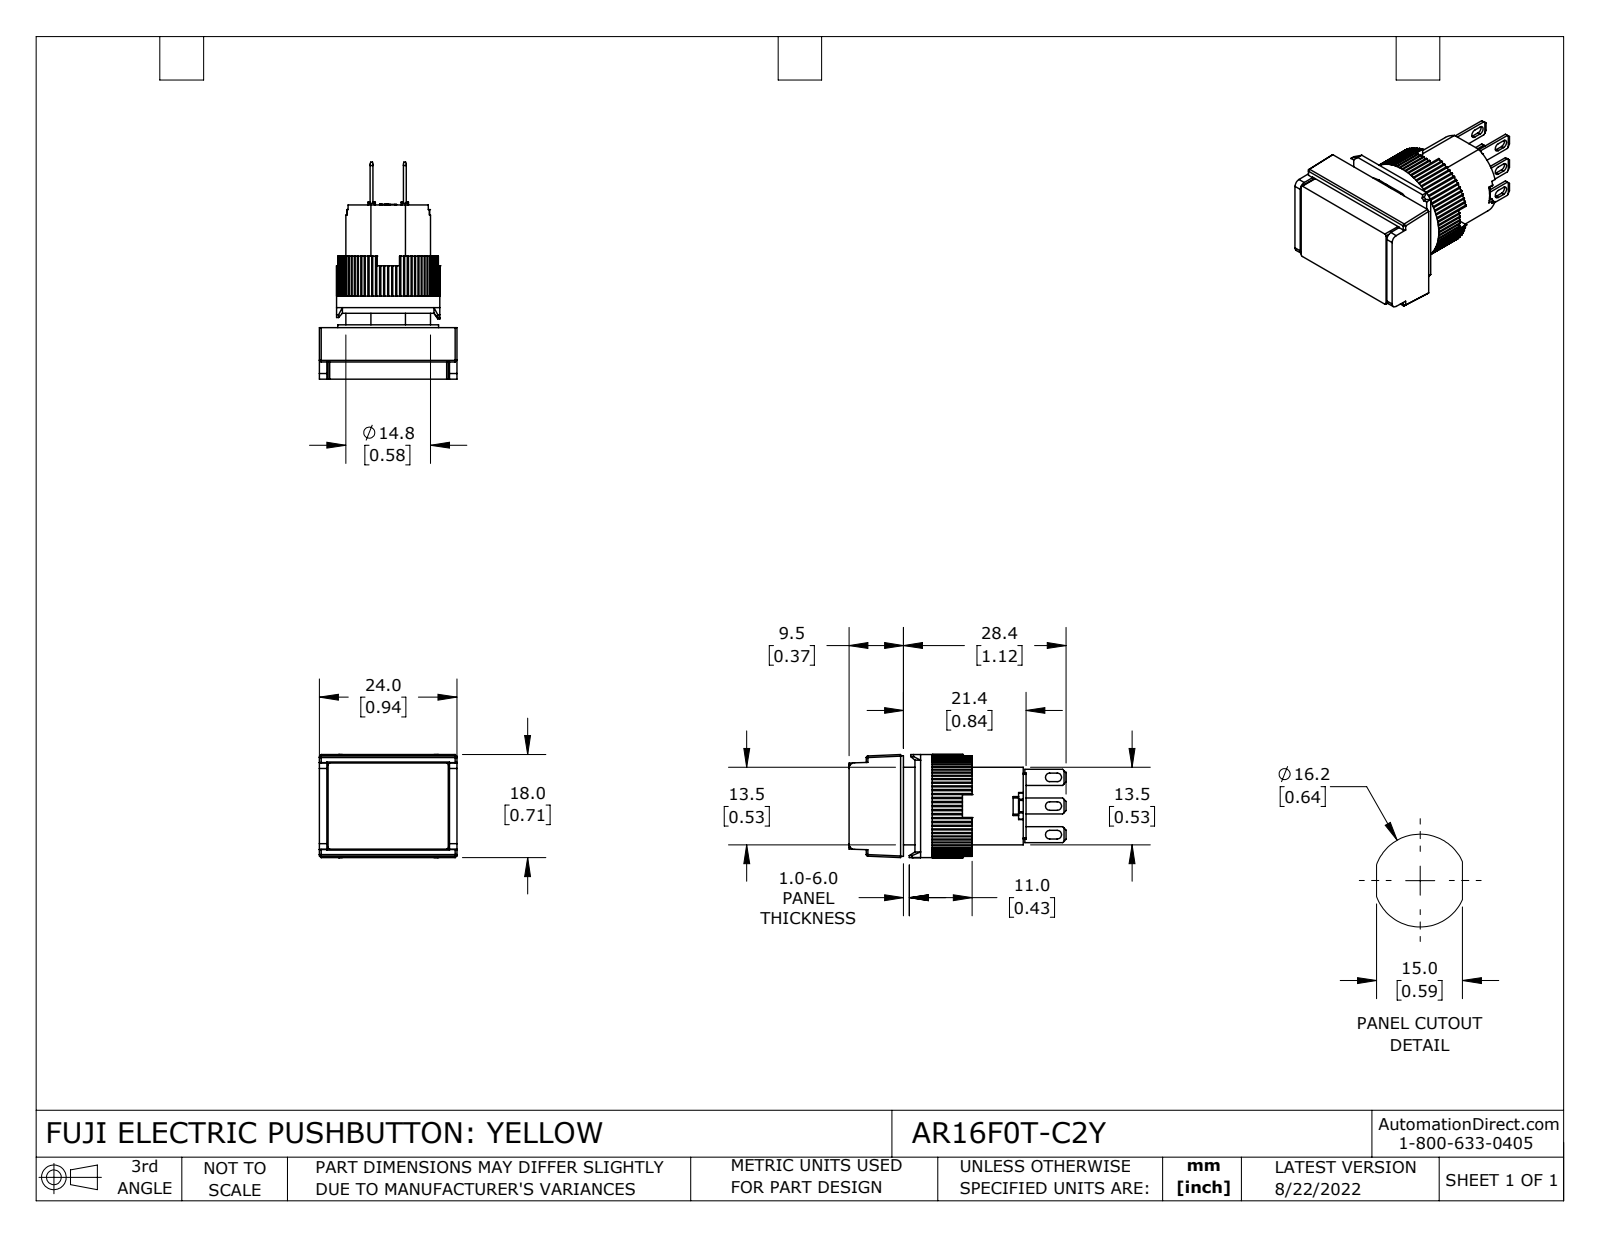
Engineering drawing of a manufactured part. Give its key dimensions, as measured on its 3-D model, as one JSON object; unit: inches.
{"part_name": "AR16F0T-C2Y", "step_written_by": "SolidWorks 2021 (CONFIG_CONTROL_DESIGN)", "units": "inches", "bodies": {"solids": 12, "faces": 813, "planar": 632, "cylindrical": 177, "other": 4}, "overall_size": [1.492, 0.945, 0.709], "volume_in3": 0.443, "surface_area_in2": 9.124, "round_holes": [[0.543, 1], [0.583, 1]], "round_bosses_or_shafts": [[0.709, 1], [0.693, 1]], "partial_cylinders_radius": [[0.01, 80], [0.008, 12], [0.012, 6], [0.03, 6], [0.039, 2]], "face_to_face_distances": [0.213, 0.354, 0.142, 0.492, 0.35, 0.138, 0.02, 0.843, 0.059, 0.453]}
